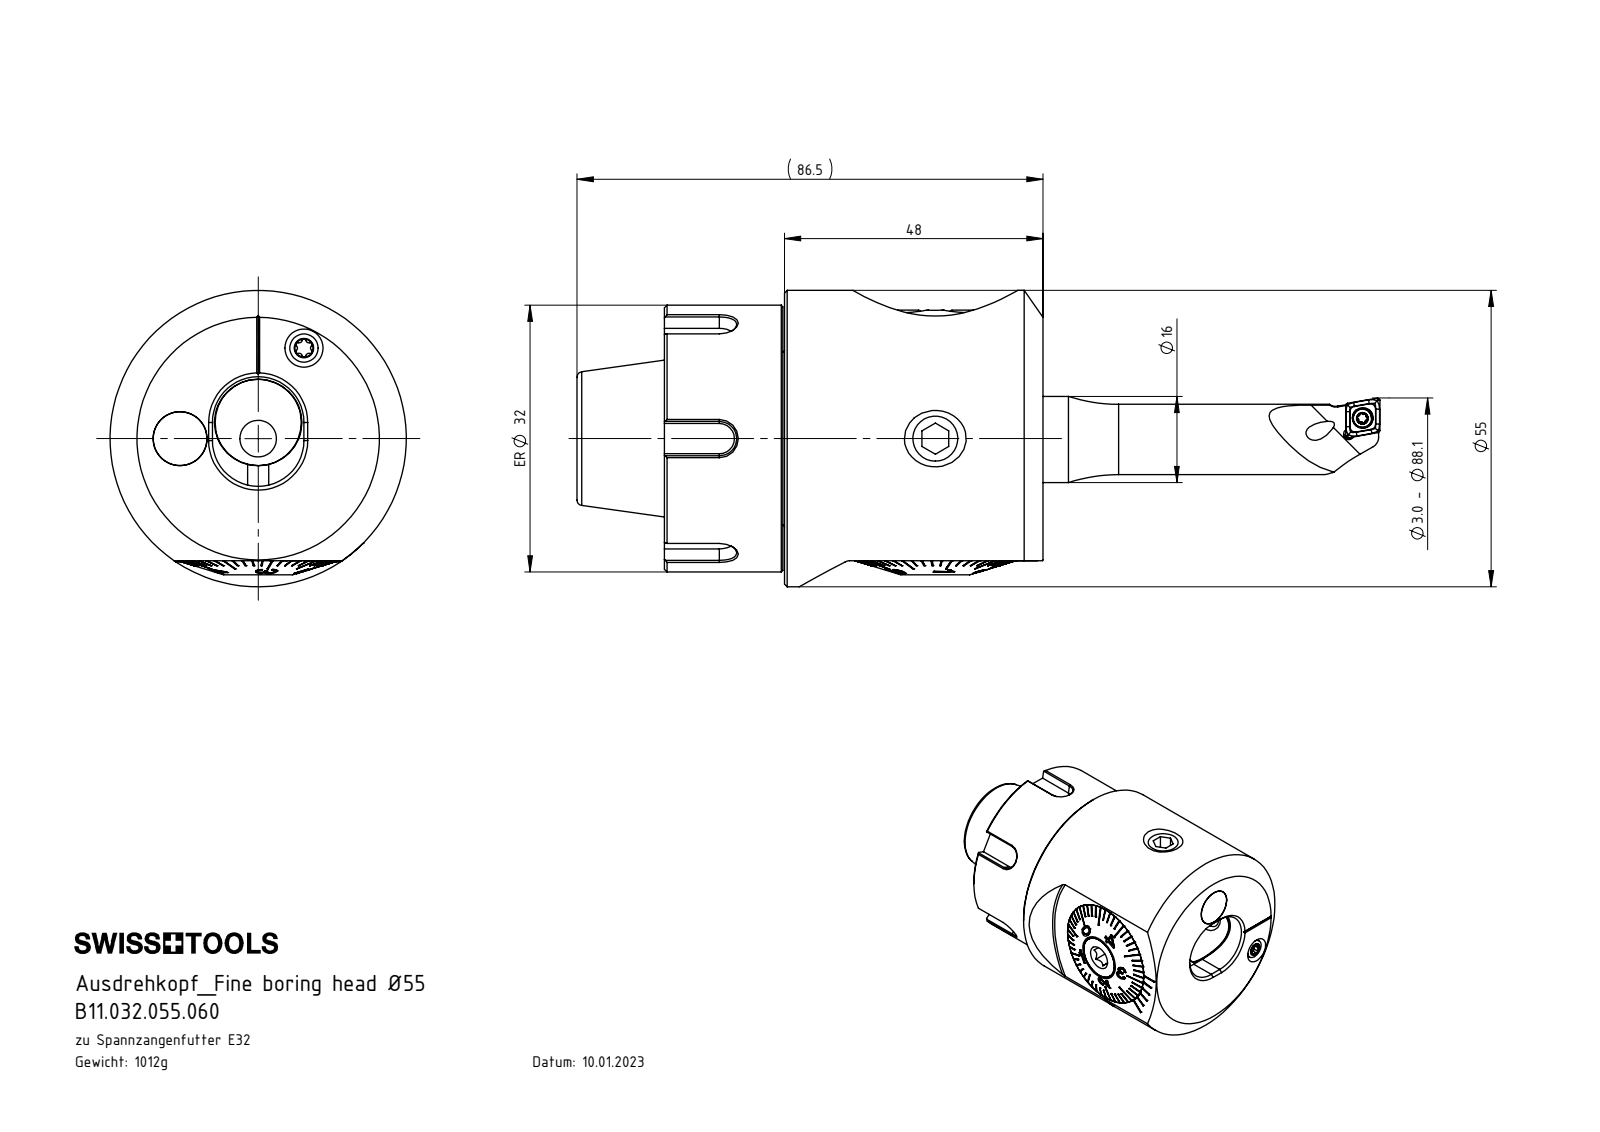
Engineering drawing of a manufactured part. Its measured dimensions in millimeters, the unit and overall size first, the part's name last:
Units: millimetres
Overall size (bounding box): 86.5 × 55 × 55
Round holes (diameter × count): ⌀8.5 ×3, ⌀1.6 ×1, ⌀3.3 ×1, ⌀4.2 ×1, ⌀6.8 ×1, ⌀8 ×1, ⌀10 ×1, ⌀11.4 ×1, ⌀12.4 ×1, ⌀14 ×1, ⌀14.2 ×1, ⌀16 ×1
Round bosses / shafts (diameter × count): ⌀10 ×3, ⌀55 ×1, ⌀49.5 ×1, ⌀32 ×1, ⌀30 ×1, ⌀29.98 ×1, ⌀29.9 ×1, ⌀29.5 ×1
Partial cylindrical surfaces — rounded edges, fillets, slot ends (radius × count): R0.34 ×6, R0.59 ×6, R1.4 ×4, R1.9 ×4, R3.2 ×3, R2 ×2, R8.5 ×2, R1 ×1
Main face-to-face distances: 48, 48.3, 6.15, 22, 2.5, 2.7, 3.35, 3.45, 8.65, 22.3
Hole centre spacings: 7.25, 14.5, 3, 14.81, 16.21, 18.83, 28.48
Volume: 129 267 mm³ · Surface area: 48 473 mm²
Bodies: 16 solids, 798 faces (351 planar, 141 cylindrical, 306 other)
Part name (STEP PRODUCT): WCB-ER2.001.009_A; A55-BG2.012.006_B; Klebstoff D10; ISO 4026 - M10 x 8 (+8 more)
STEP written by: SolidWorks 2022 (AUTOMOTIVE_DESIGN)
